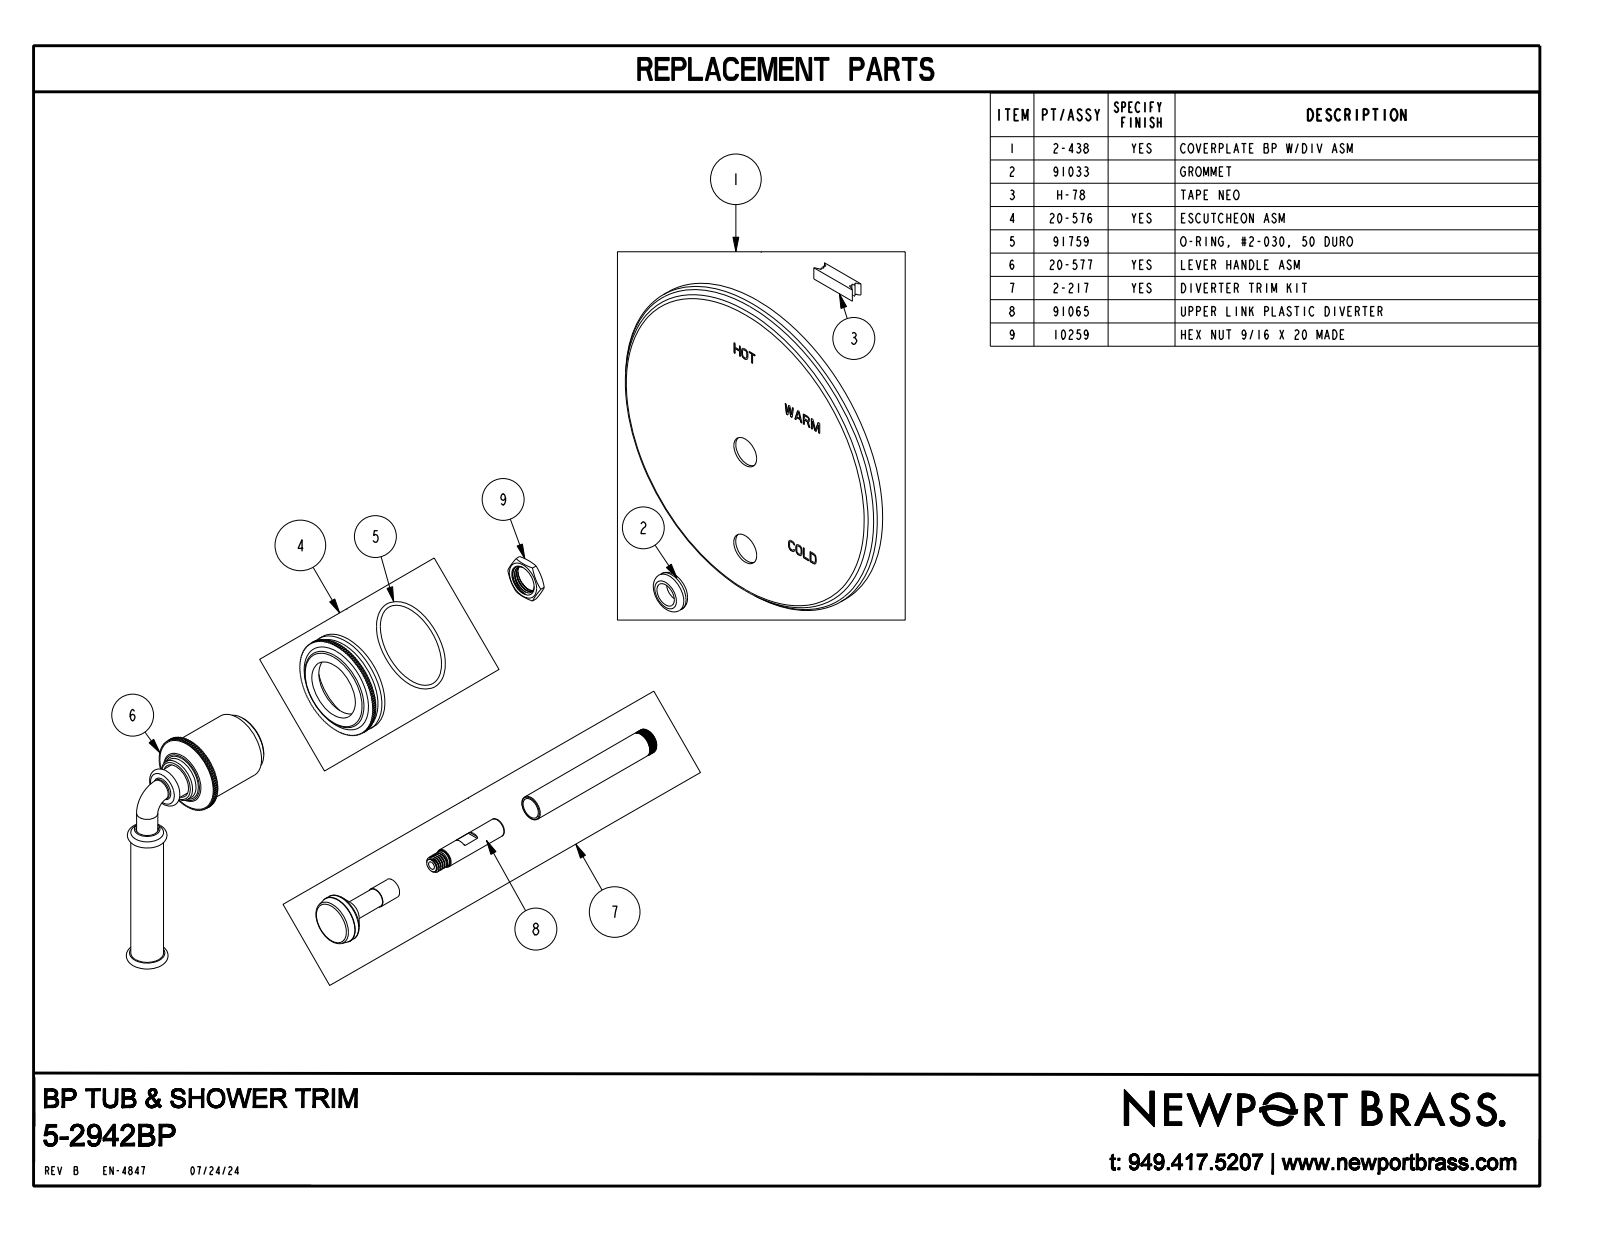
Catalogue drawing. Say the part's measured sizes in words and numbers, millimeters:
The part is named "5-2942BP". Its 3-D file was written by "CREO PARAMETRIC BY PTC INC, 2019352 (CONFIG_CONTROL_DESIGN)". It is 2 solids with 1022 faces: 711 planar, 253 cylindrical and 58 other. Overall it measures 174.1 by 165.1 by 87 millimeters. Its volume is 101 400 cubic millimeters and its surface area 63 140 square millimeters. Round holes: 1 of diameter 10, 1 of diameter 10.4, 1 of diameter 15, 1 of diameter 15.1, 1 of diameter 162.6. Round bosses or shafts: 2 of diameter 9.9, 1 of diameter 165.1, 1 of diameter 48.3, 1 of diameter 45.7, 1 of diameter 31.8, 1 of diameter 30.5, 1 of diameter 22.9, 1 of diameter 20.3. Partial cylindrical surfaces (rounded edges, fillets, slot ends): 1 of radius 18.2. The main face-to-face distances are 1.3, 6.7, 8, 7.9, 15.8, 9.1, 17.6, 10.9, 9.7, 1.8. The hole center spacings are 55, 55.1.
